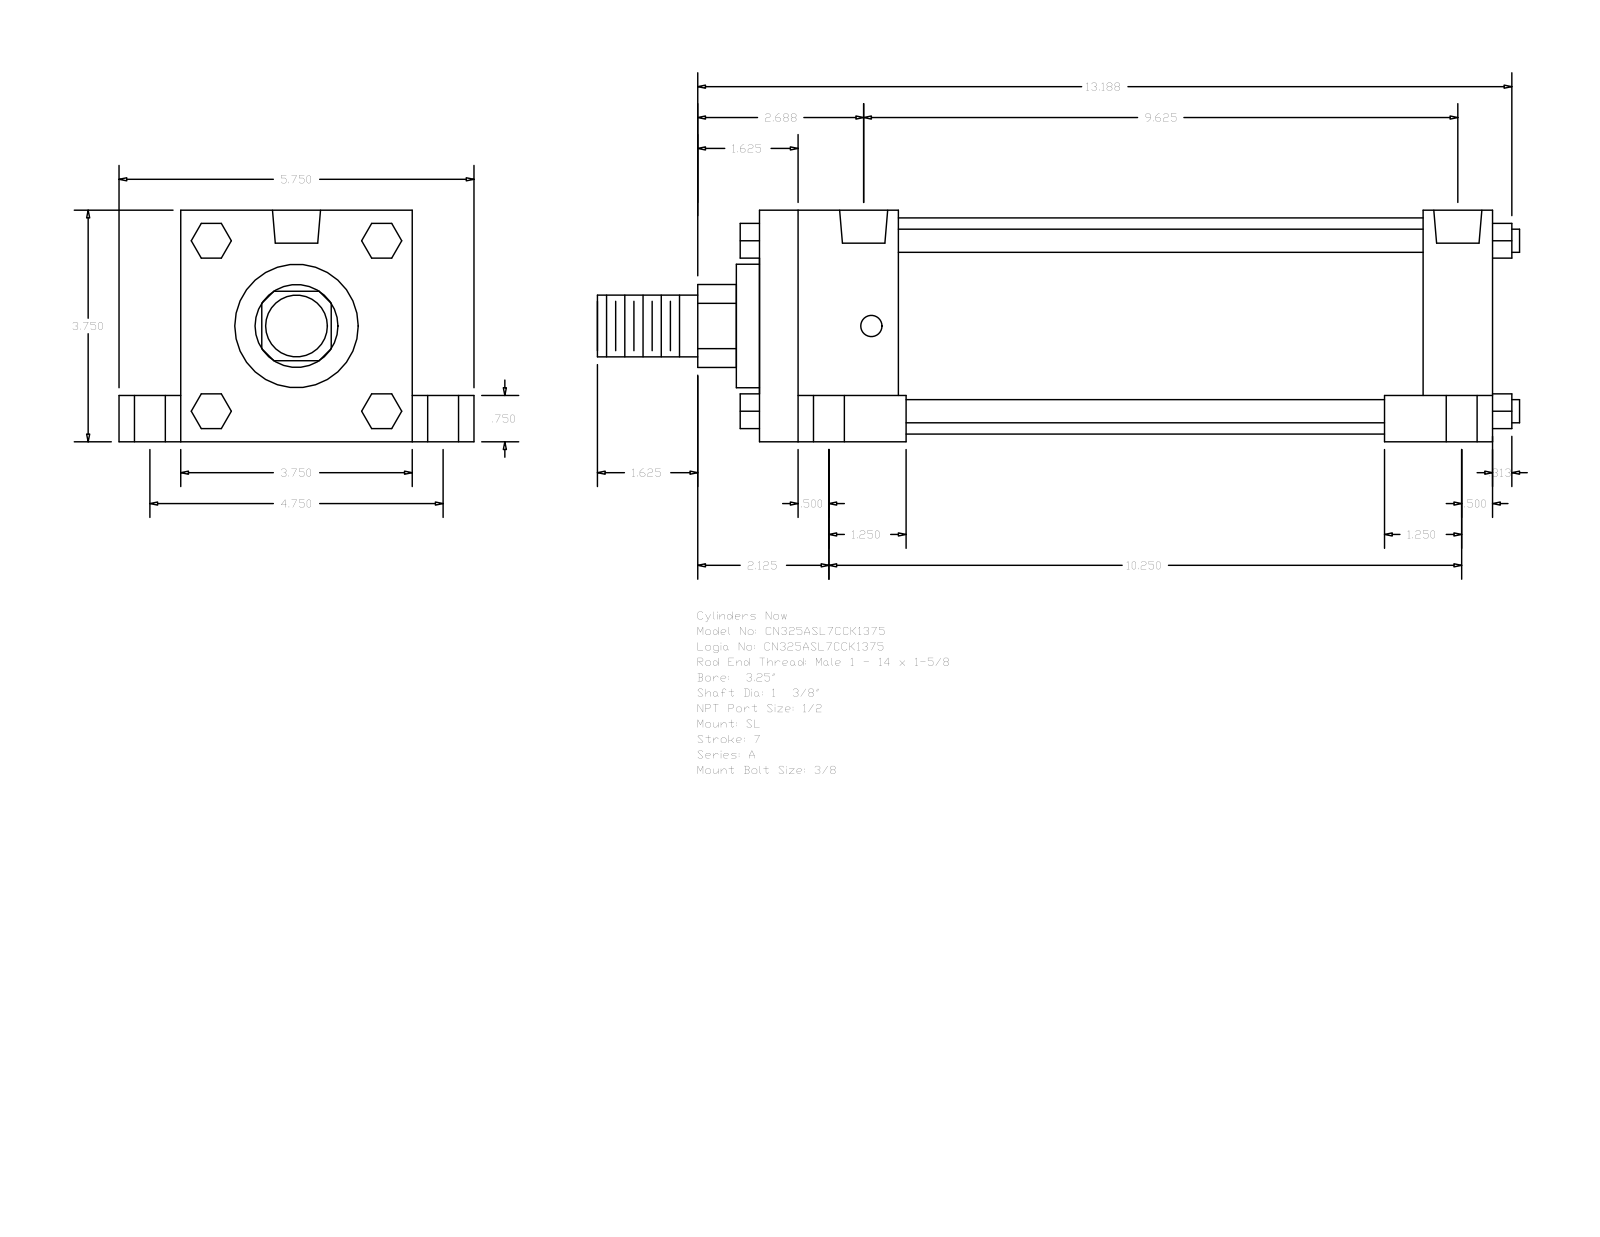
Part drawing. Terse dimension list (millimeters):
name: A_SL__0325_1.375
written by: GSSL Pune (CONFIG_CONTROL_DESIGN)
unit: mm
bodies: 0 solids, 150 faces (114 planar, 36 cylindrical, 0 other)
size: 379.41 × 146.05 × 95.25
holes: 4× ⌀8.73, 4× ⌀12.7, 4× ⌀19.05, 2× ⌀19.77
bosses: 4× ⌀9.53, 1× ⌀88.9, 1× ⌀50.8, 1× ⌀34.92, 1× ⌀25.4
rounds: 1× R17.06
face distances: 95.24, 301.62, 25.41, 120.65, 19.05, 76.19, 57.15, 28.57, 273.05, 215.9
hole spacings: 3.18, 60.35, 60.52, 62, 62.81, 120.66, 238.12, 241.3
